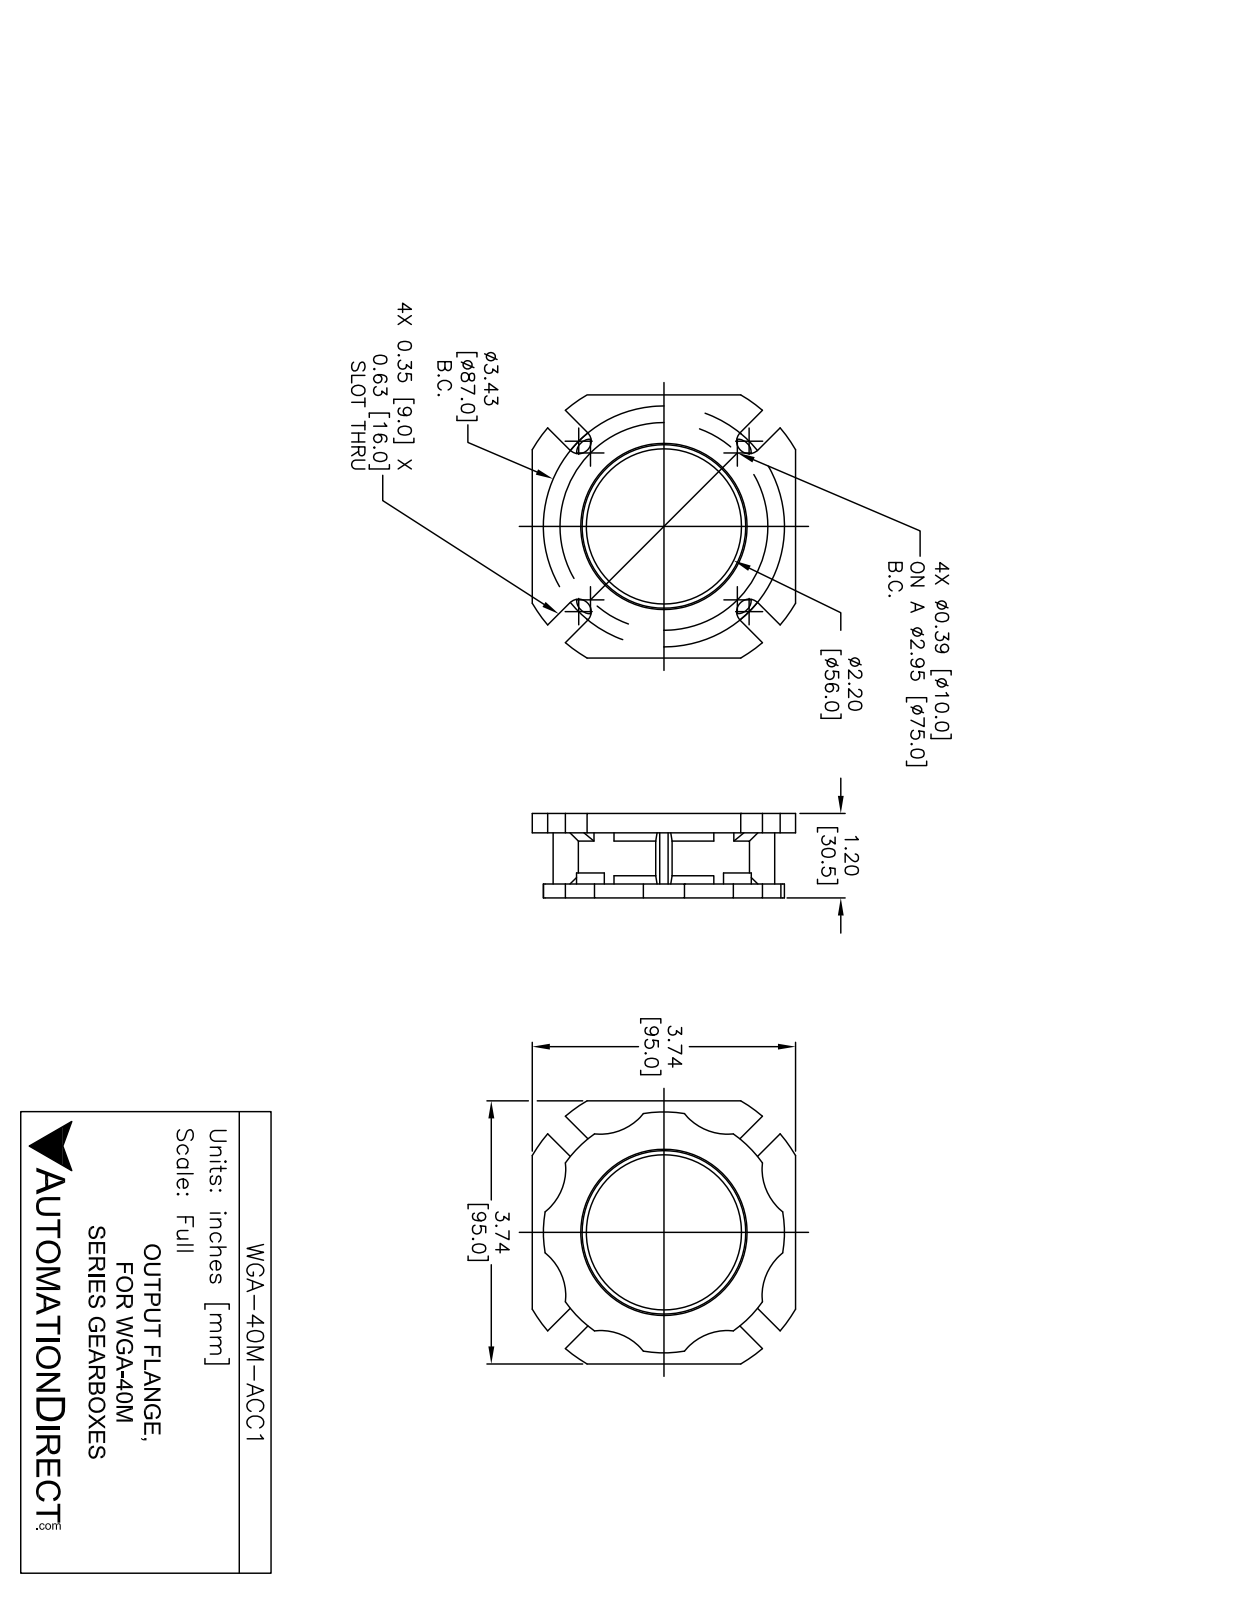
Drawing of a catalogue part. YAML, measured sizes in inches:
part_name: "WGA-40M-ACC1"
step_written_by: "SolidWorks 2014 (AUTOMOTIVE_DESIGN)"
units: inches
bodies: {solids: 1, faces: 122, planar: 51, cylindrical: 53, other: 18}
overall_size: [3.74, 3.74, 1.201]
volume: 4.009
surface_area: 46.77
round_holes:
  - {diameter: 2.205, count: 1}
  - {diameter: 2.323, count: 1}
  - {diameter: 2.362, count: 1}
round_bosses_or_shafts:
  - {diameter: 0.394, count: 4}
  - {diameter: 2.441, count: 1}
partial_cylinders:
  - {radius: 0.787, count: 8}
  - {radius: 0.177, count: 4}
  - {radius: 1.713, count: 1}
  - {radius: 2.165, count: 1}
face_to_face_distances: [0.276, 0.925, 1.201, 0.197, 0.728, 1.004, 3.74, 0.157, 0.608, 0.354]
